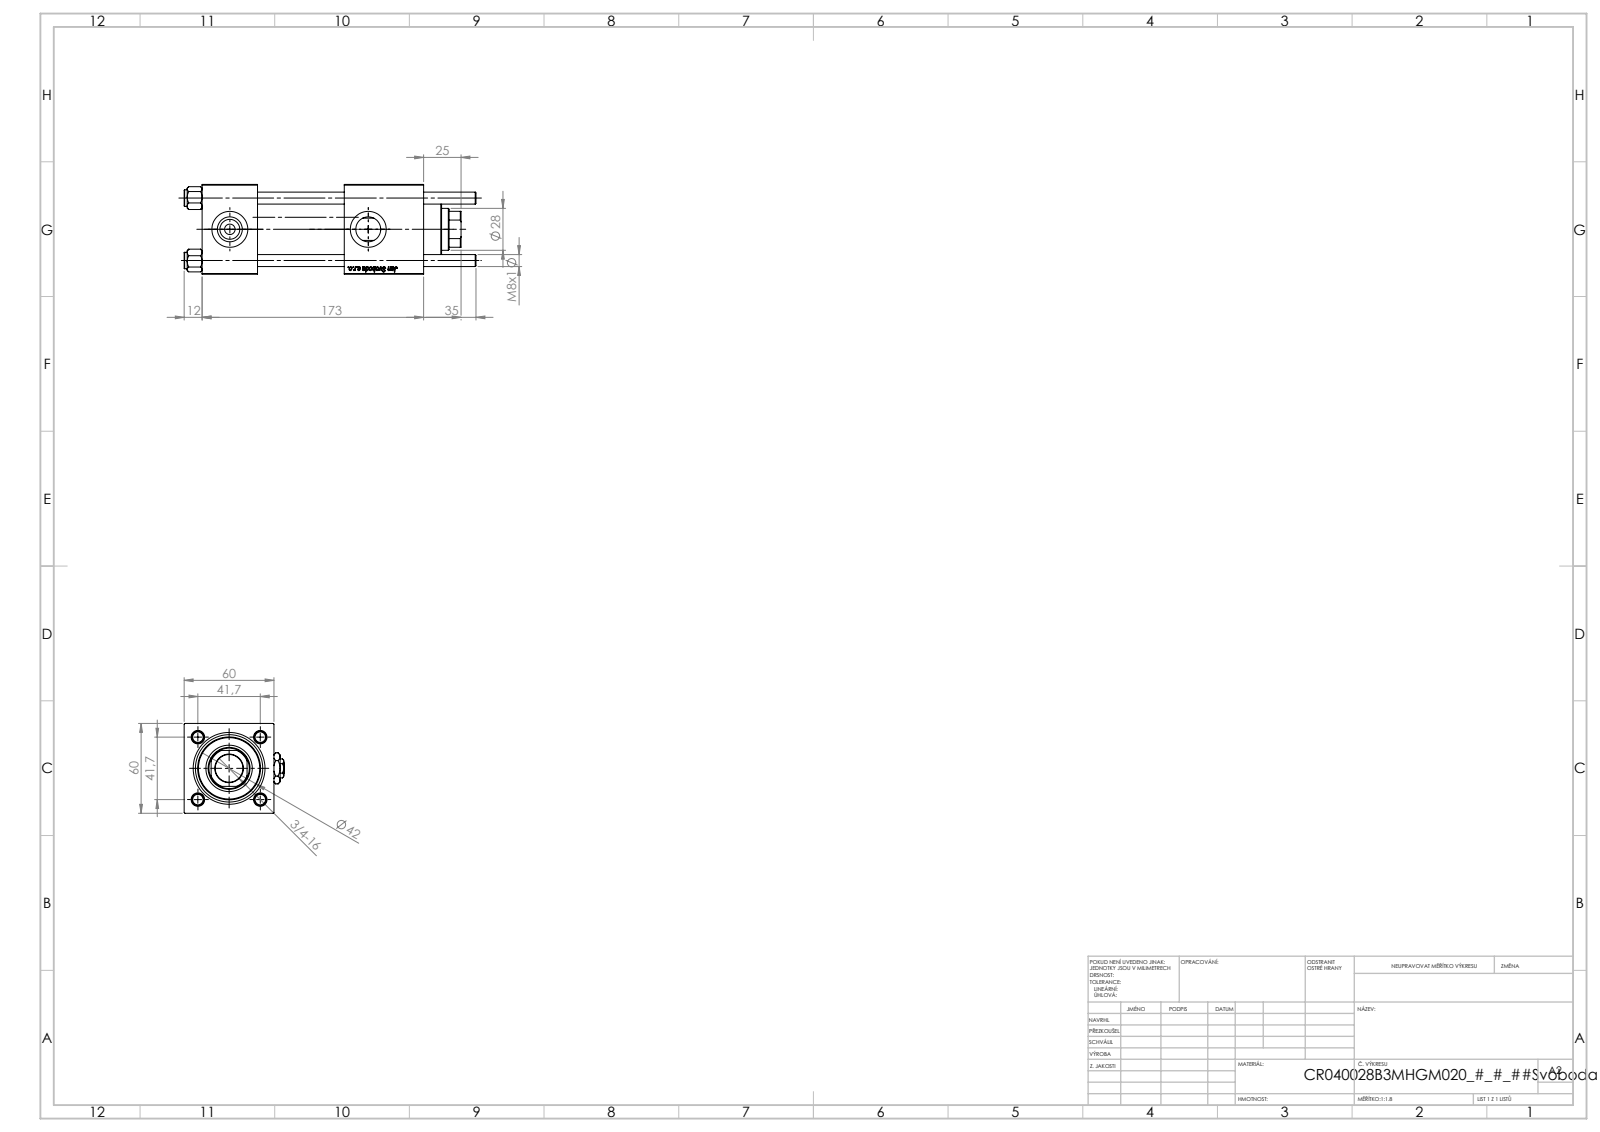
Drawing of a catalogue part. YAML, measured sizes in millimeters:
part_name: "V215_VC_A; NUT_M5_B; V215CR_VCP_B; V215CR_B_TYCINKA (+2 more)"
step_written_by: "SolidWorks 2019 (CONFIG_CONTROL_DESIGN)"
units: millimeters
bodies: {solids: 13, faces: 1259, planar: 481, cylindrical: 88, other: 690}
overall_size: [195, 67, 60]
volume: 432328
surface_area: 122775
round_holes:
  - {diameter: 8, count: 4}
  - {diameter: 7, count: 2}
  - {diameter: 16.66, count: 2}
  - {diameter: 24, count: 2}
  - {diameter: 18.5, count: 1}
  - {diameter: 28, count: 1}
  - {diameter: 31, count: 1}
  - {diameter: 40, count: 1}
  - {diameter: 45, count: 1}
round_bosses_or_shafts:
  - {diameter: 11, count: 4}
  - {diameter: 46, count: 1}
  - {diameter: 42, count: 1}
partial_cylinders:
  - {radius: 13.5, count: 1}
face_to_face_distances: [60, 37, 58, 95, 53, 119.3, 82.3, 24.3, 148, 111]
hole_center_spacings: [29.49, 41.7, 58.97, 92.5]
